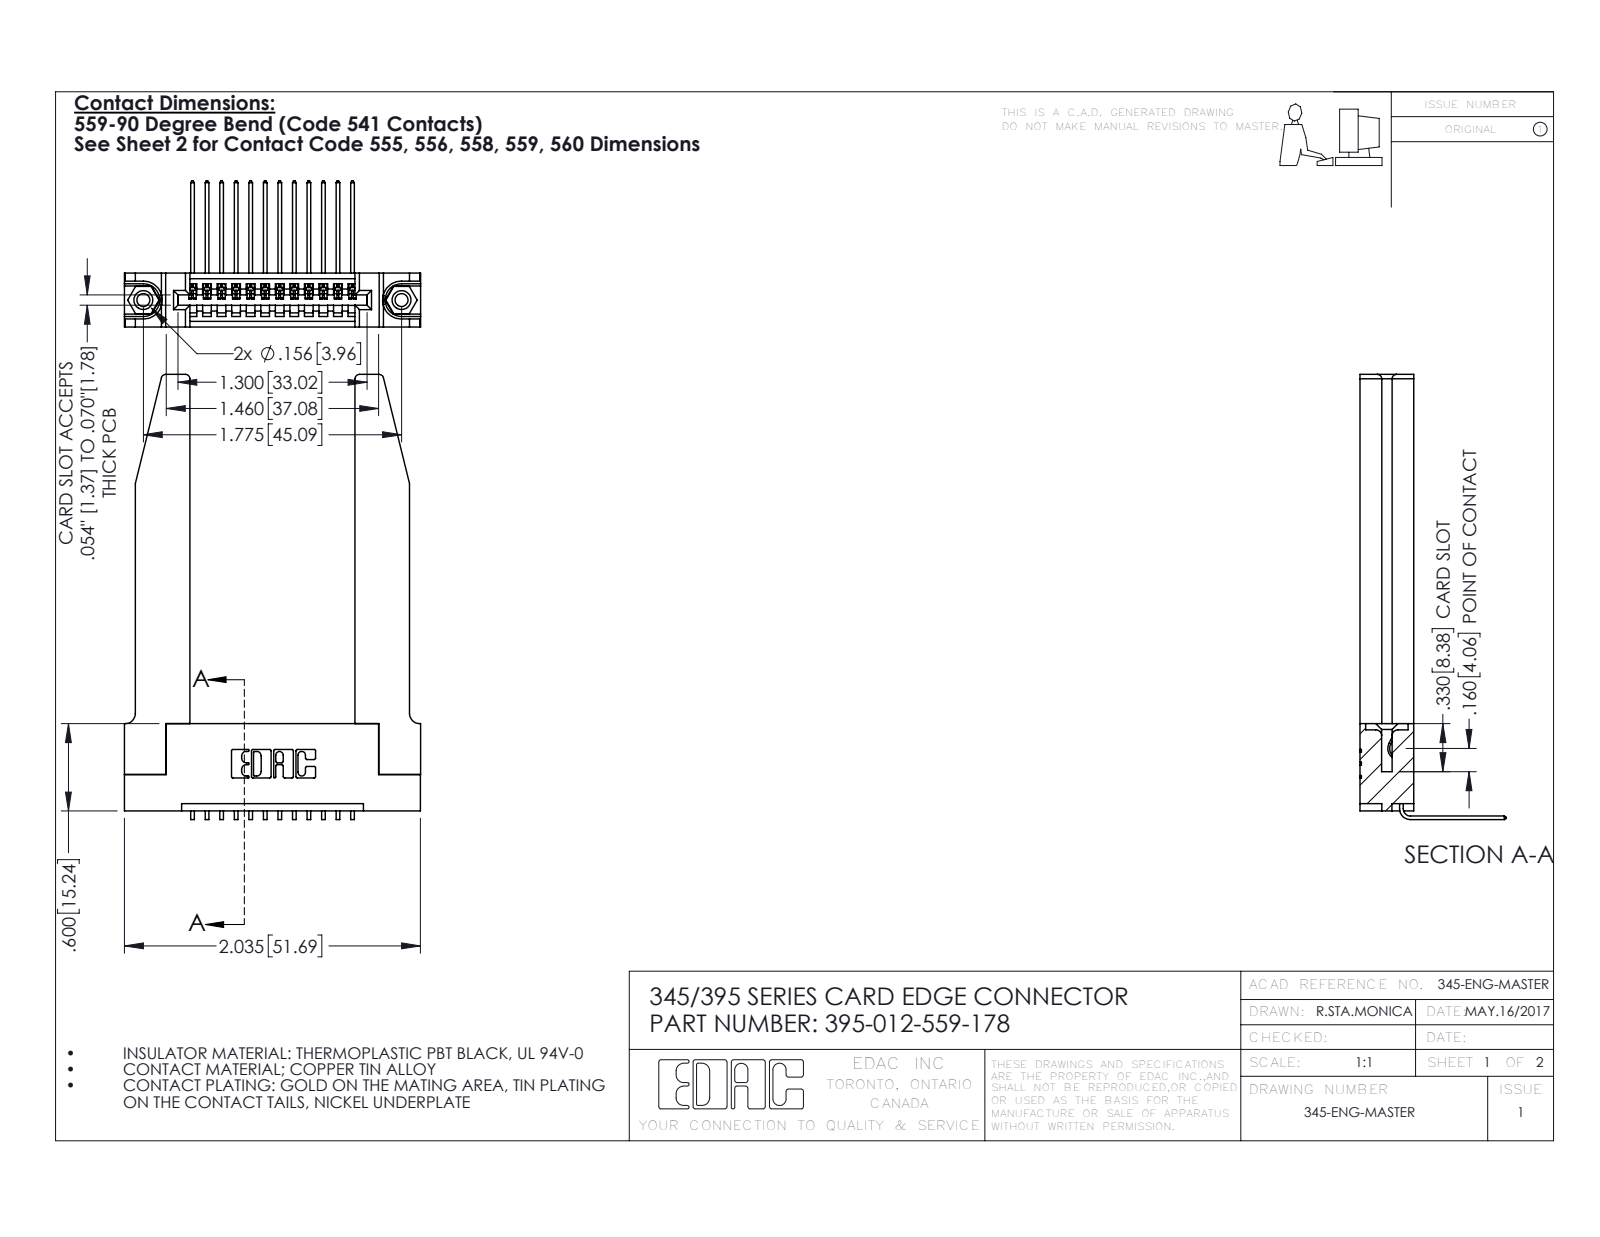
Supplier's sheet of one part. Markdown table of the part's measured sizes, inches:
| quantity | value |
| --- | --- |
| part name | 345-220-078_345-220-078; 345 Part_Flush Mounting Lugs - 0.156 Dia-TH; 345-250-001_345-250-001-102; 345-292-001_558 559 Tail - 1 (+1 more) |
| STEP written by | SolidWorks 2016 (CONFIG_CONTROL_DESIGN) |
| units | inches |
| bodies | 17 solids, 1080 faces (726 planar, 302 cylindrical, 52 other) |
| overall size | 3.059 × 2.036 × 1.005 |
| volume | 0.761 in³ |
| surface area | 20.04 in² |
| round holes (diameter × count) | 0.089 × 2, 0.125 × 2, 0.156 × 2, 0.064 × 1 |
| round bosses / shafts (diameter × count) | 0.155 × 2 |
| partial cylindrical surfaces (radius × count) | 0.006 × 24, 0.01 × 22, 0.03 × 8, 0.007 × 6, 0.031 × 6, 0.026 × 3, 0.031 × 2, 0.04 × 2 |
| main face-to-face distances | 0.37, 0.072, 0.298, 0.2, 0.15, 0.148, 0.077, 0.22, 1.135, 0.098 |
| hole center spacings | 0.27, 1.543, 1.775 |
